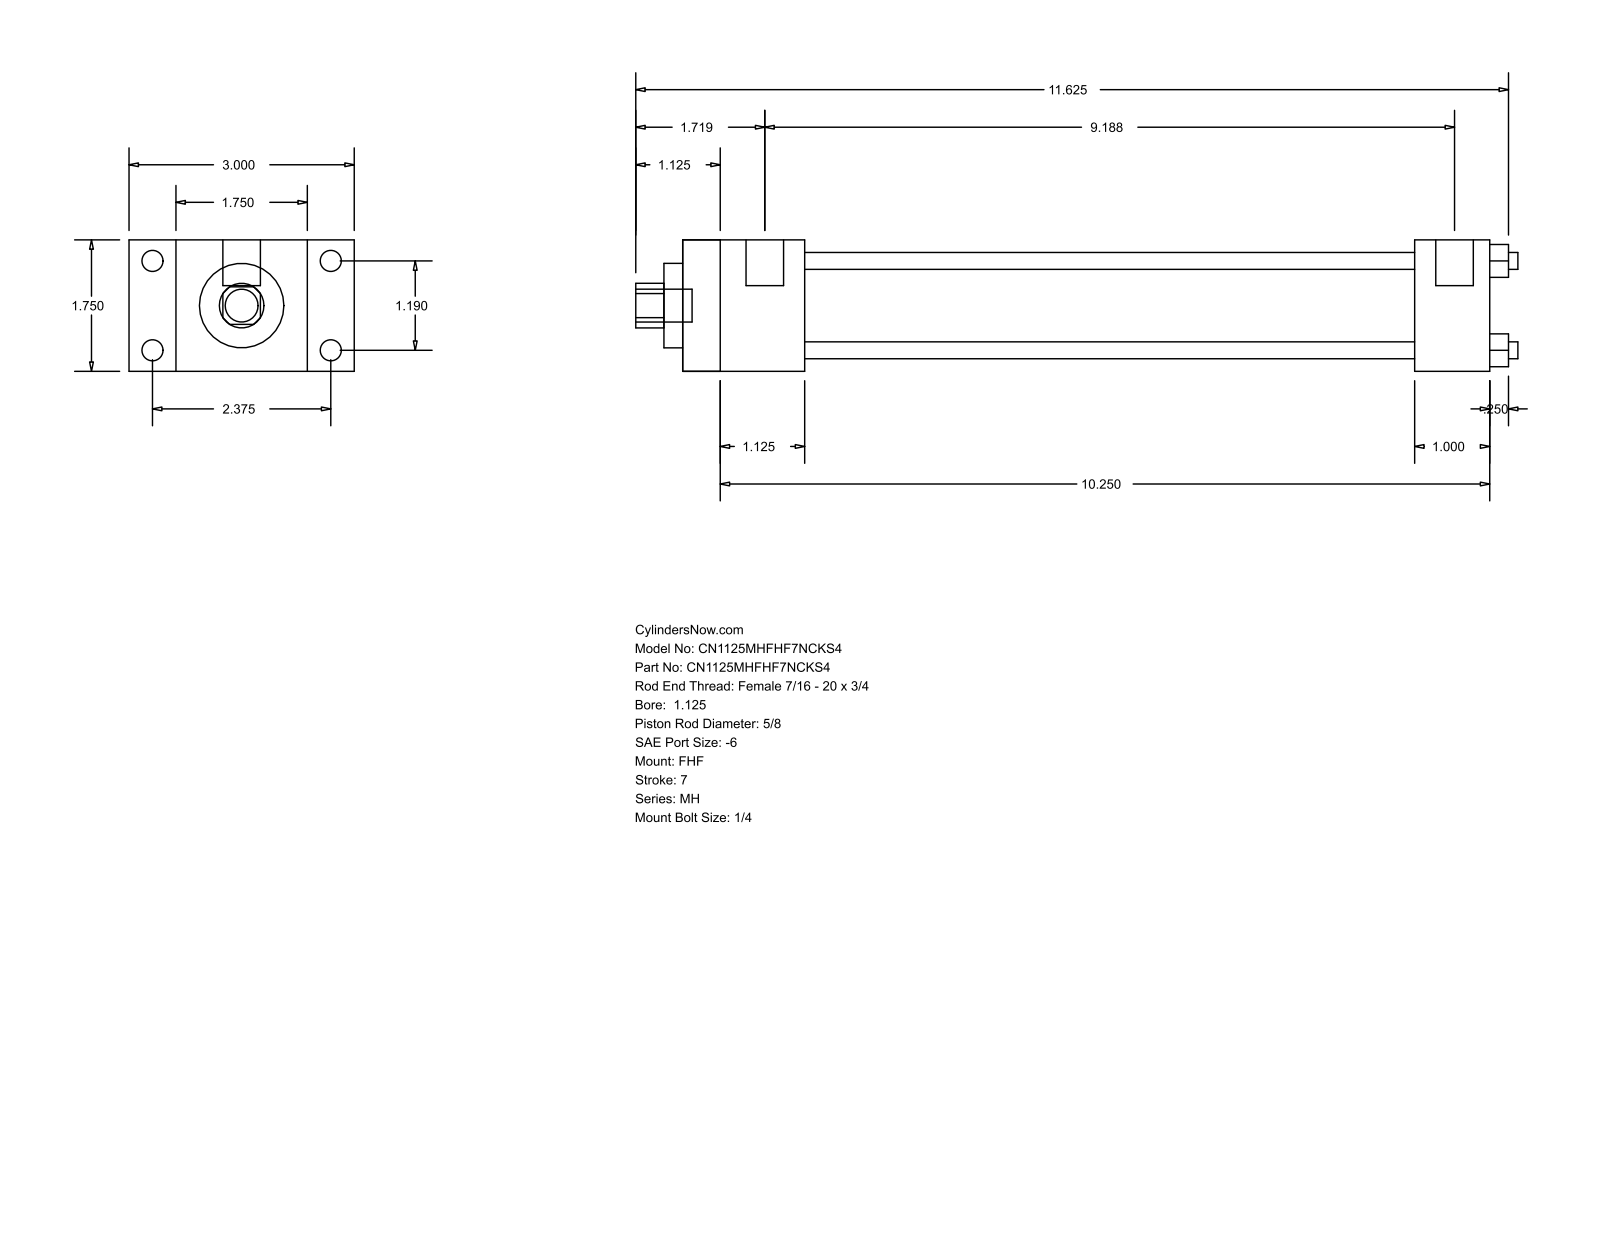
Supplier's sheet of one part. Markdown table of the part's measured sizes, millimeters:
| quantity | value |
| --- | --- |
| part name | MH_FHF__0112_0.625 |
| STEP written by | GSSL Pune (CONFIG_CONTROL_DESIGN) |
| units | millimeters |
| bodies | 0 solids, 88 faces (60 planar, 28 cylindrical, 0 other) |
| overall size | 298.45 × 76.2 × 44.45 |
| round holes (diameter × count) | 5.71 × 4, 15.88 × 1, 28.57 × 1, 34.92 × 1 |
| round bosses / shafts (diameter × count) | 7.14 × 4, 5.56 × 4, 12.7 × 2, 11.11 × 1 |
| partial cylindrical surfaces (radius × count) | 7.54 × 1 |
| main face-to-face distances | 44.46, 15.87, 60.33, 41.27, 76.2, 273.05, 231.78, 247.64, 206.37, 25.41 |
| hole center spacings | 21.37, 30.22, 42.74 |
